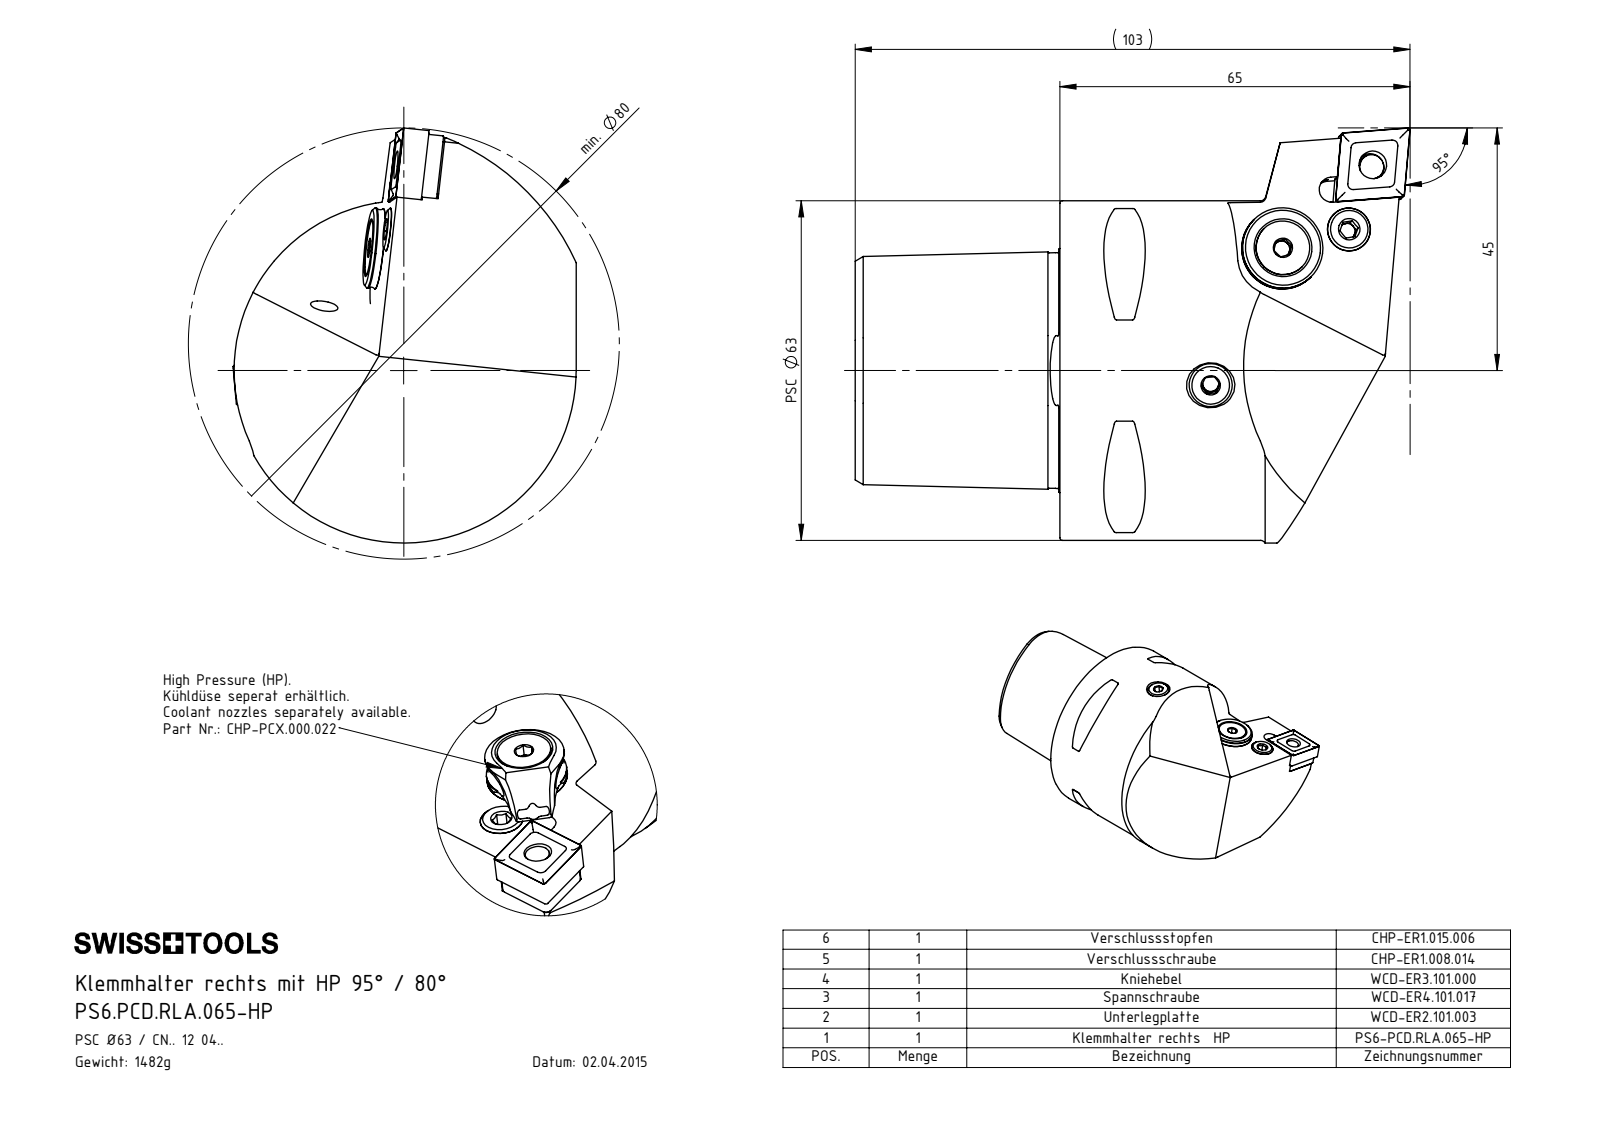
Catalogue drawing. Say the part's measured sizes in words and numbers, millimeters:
The part is named "CHP-ER1.015.006; ISO 8752 2x8; PS6-PCD.RLA.065-HP_B; WCD (+8 more)". Its 3-D file was written by "SolidWorks 2017 (AUTOMOTIVE_DESIGN)". It is 11 solids with 450 faces: 133 planar, 117 cylindrical and 200 other. Overall it measures 103 by 77 by 63.69 millimeters. Its volume is 186 975 cubic millimeters and its surface area 34 345 square millimeters. Round holes: 2 of diameter 4.2, 2 of diameter 5, 2 of diameter 7, 1 of diameter 1.2, 1 of diameter 2, 1 of diameter 2.5, 1 of diameter 3, 1 of diameter 4, 1 of diameter 5.16, 1 of diameter 5.2, 1 of diameter 6.4, 1 of diameter 8.1. Round bosses or shafts: 2 of diameter 8, 1 of diameter 63, 1 of diameter 15, 1 of diameter 13.4, 1 of diameter 10, 1 of diameter 7.9, 1 of diameter 6.4, 1 of diameter 5.5. Partial cylindrical surfaces (rounded edges, fillets, slot ends): 10 of radius 0.5, 4 of radius 0.4, 4 of radius 1, 2 of radius 2.5, 1 of radius 2.1, 1 of radius 2.2, 1 of radius 2.35, 1 of radius 2.8. The main face-to-face distances are 38, 24.88, 4.5, 27, 11, 4.46, 55.8, 3.14, 3.18, 7.64. The hole center spacings are 4.5, 11.97, 13.08, 19.85, 19.91, 23.12, 12.79, 12.85.
